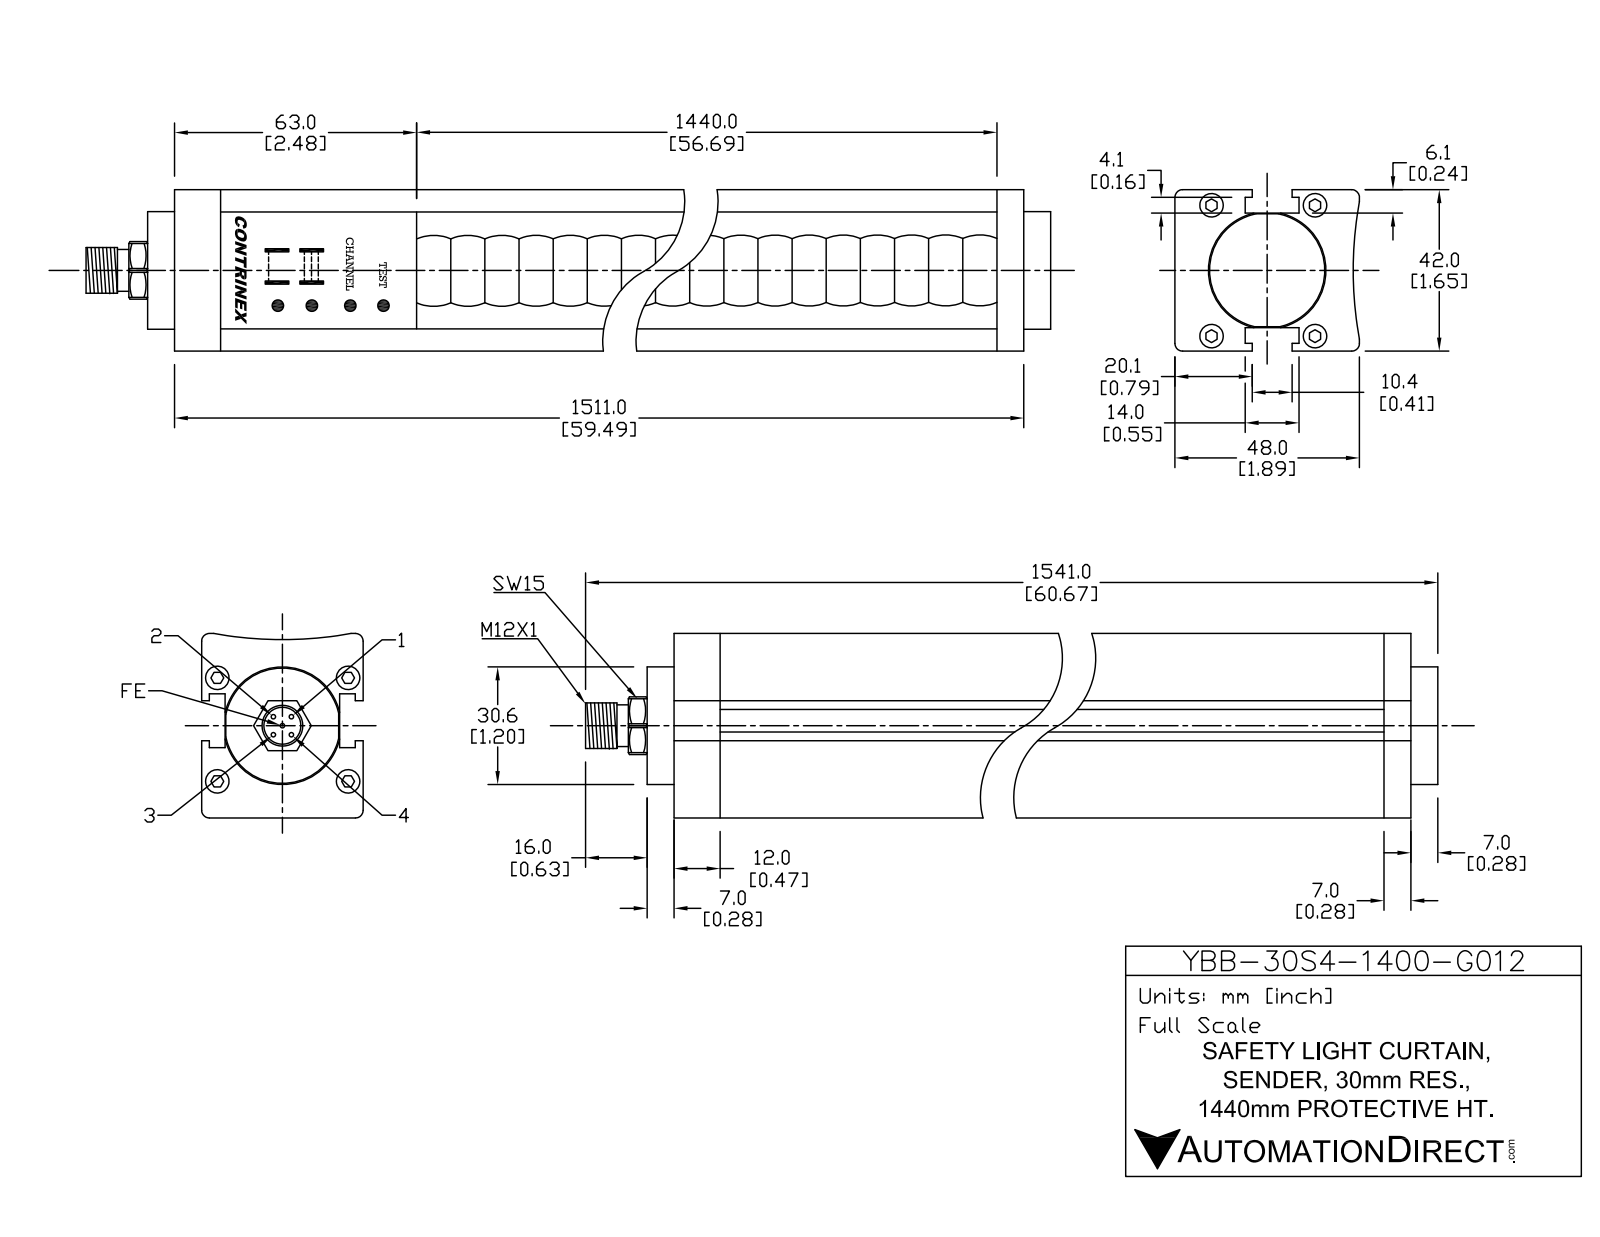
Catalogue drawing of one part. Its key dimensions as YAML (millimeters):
part_name: "YBB-30S4-1400-G012"
step_written_by: "SolidWorks 2016 (AUTOMOTIVE_DESIGN)"
units: millimeters
bodies: {solids: 19, faces: 440, planar: 208, cylindrical: 168, other: 64}
overall_size: [1541, 48, 42]
volume: 2715000
surface_area: 339791
round_holes:
  - {diameter: 6, count: 4}
  - {diameter: 8.5, count: 1}
  - {diameter: 32, count: 1}
round_bosses_or_shafts:
  - {diameter: 1, count: 5}
  - {diameter: 5.5, count: 4}
  - {diameter: 30.6, count: 1}
  - {diameter: 12, count: 1}
  - {diameter: 10.5, count: 1}
partial_cylinders:
  - {radius: 1, count: 48}
  - {radius: 0.5, count: 4}
  - {radius: 0.55, count: 2}
  - {radius: 8.2, count: 1}
  - {radius: 100, count: 1}
face_to_face_distances: [6.3, 35.7, 42, 29.4, 14, 17.2, 31.2, 15.7, 29.7, 46.9]
hole_center_spacings: [21.04, 22.34, 26.9, 34, 43.35]
